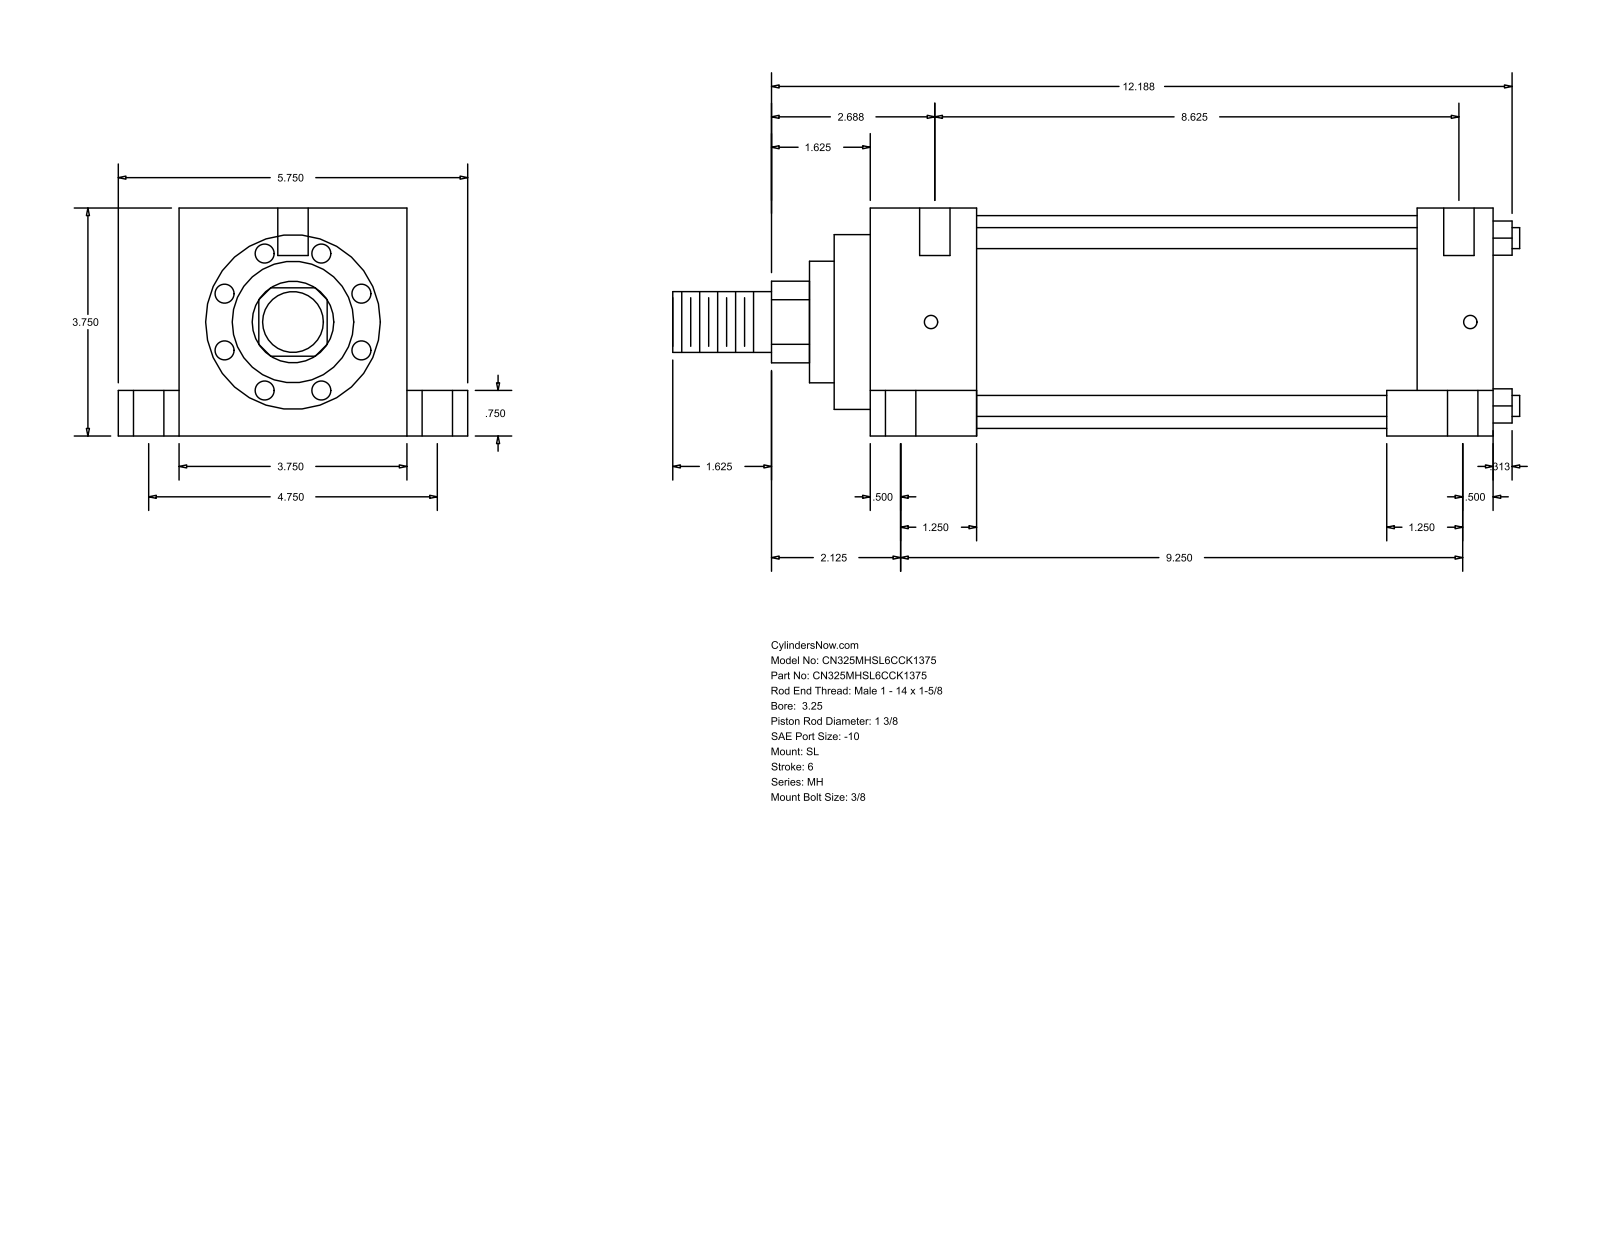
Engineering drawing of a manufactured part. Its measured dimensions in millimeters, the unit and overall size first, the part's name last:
Units: millimetres
Overall size (bounding box): 354.01 × 146.05 × 95.25
Round holes (diameter × count): ⌀12.7 ×6, ⌀5.56 ×4, ⌀19.05 ×4
Round bosses / shafts (diameter × count): ⌀8.76 ×4, ⌀88.9 ×1, ⌀73.03 ×1, ⌀50.8 ×1, ⌀34.92 ×1, ⌀25.4 ×1
Partial cylindrical surfaces — rounded edges, fillets, slot ends (radius × count): R17.06 ×1
Main face-to-face distances: 95.24, 260.35, 44.45, 215.9, 25.41, 120.65, 19.05, 76.19, 228.61, 184.16
Hole centre spacings: 60.35, 60.41, 61.65, 62, 120.66, 225.43, 228.77, 230.3
Bodies: 0 solids, 110 faces (77 planar, 33 cylindrical, 0 other)
Part name (STEP PRODUCT): MH_SL__0325_1.375
STEP written by: GSSL Pune (CONFIG_CONTROL_DESIGN)
